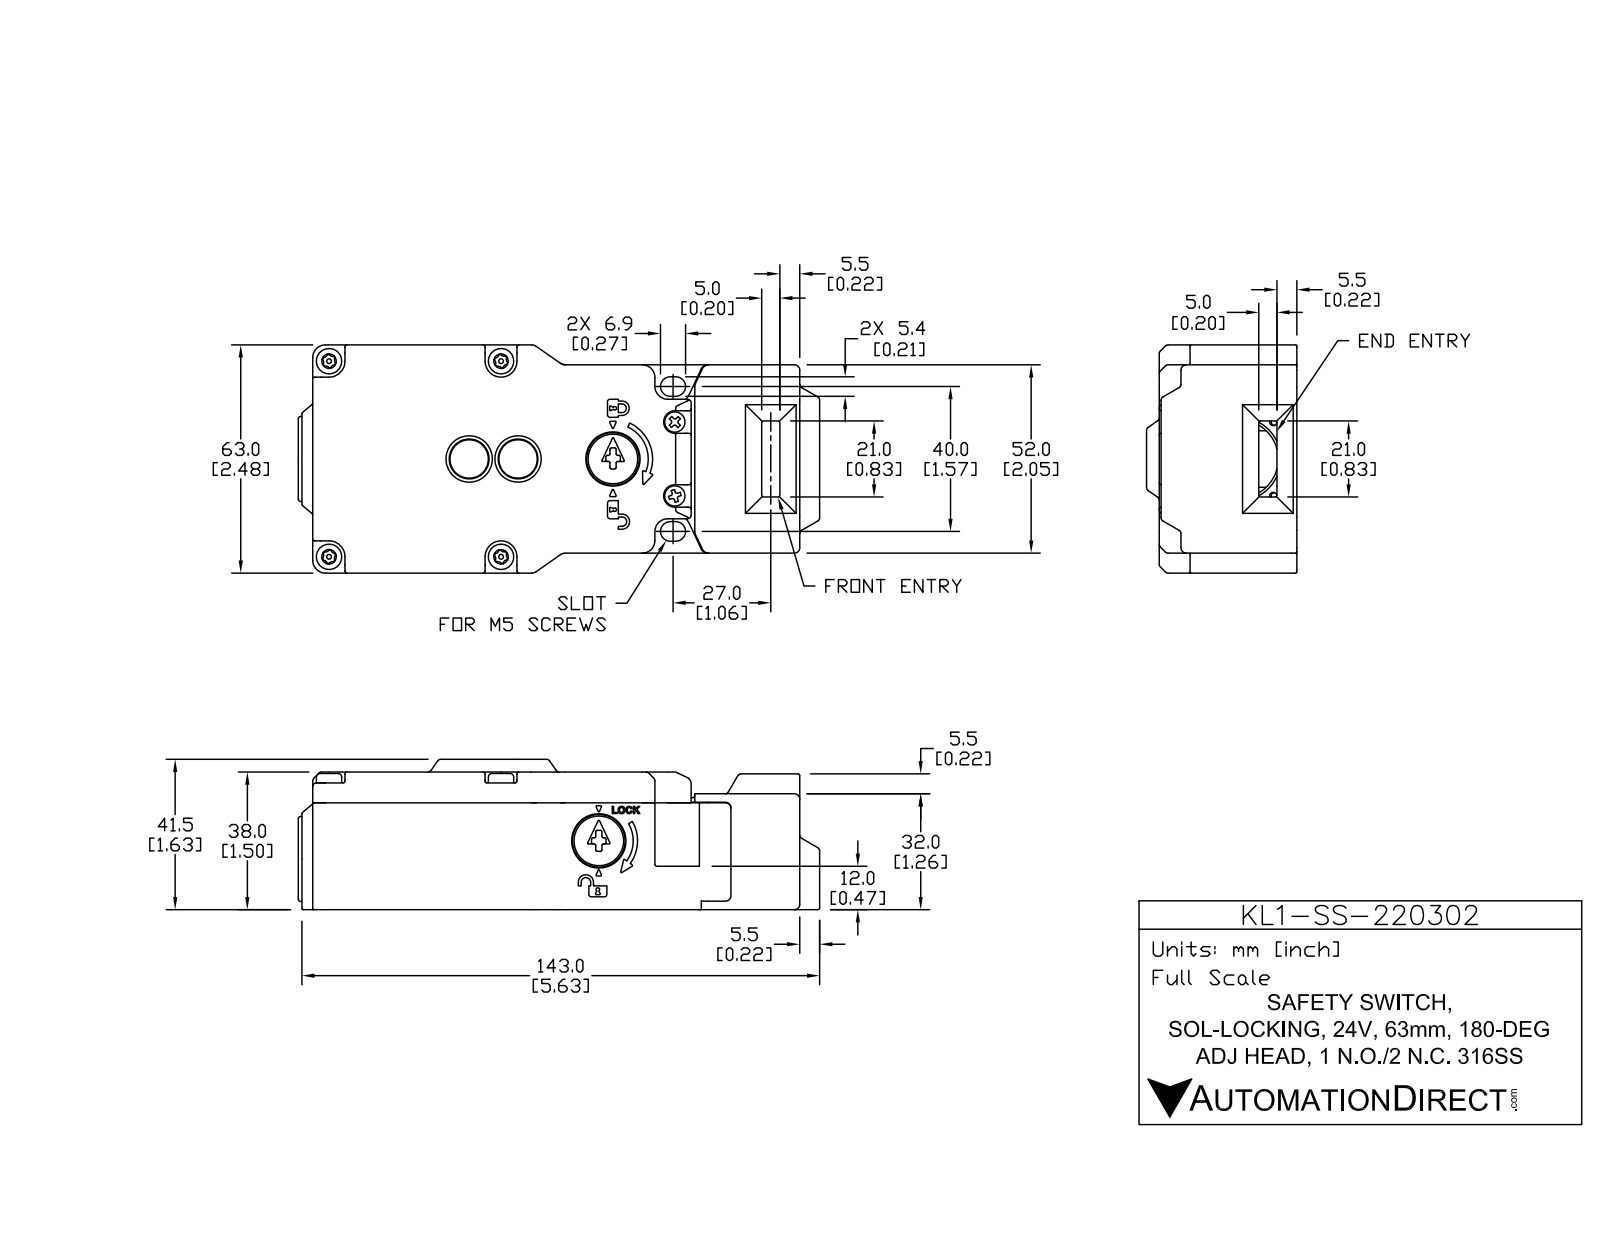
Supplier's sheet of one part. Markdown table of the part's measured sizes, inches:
| quantity | value |
| --- | --- |
| part name | KL1-SS-220302 |
| STEP written by | SolidWorks 2017 (AUTOMOTIVE_DESIGN) |
| units | inches |
| bodies | 18 solids, 3047 faces (909 planar, 1225 cylindrical, 913 other) |
| overall size | 5.669 × 2.48 × 1.634 |
| volume | 6.348 in³ |
| surface area | 118.8 in² |
| round holes (diameter × count) | 0.102 × 4, 0.134 × 4, 0.157 × 4, 0.161 × 4, 0.177 × 4, 0.197 × 4, 0.079 × 2, 0.083 × 2, 0.118 × 2, 0.126 × 2, 0.142 × 2, 0.264 × 2 |
| round bosses / shafts (diameter × count) | 0.276 × 4, 0.138 × 4, 0.051 × 4, 0.197 × 3, 0.039 × 3, 0.571 × 2, 0.417 × 2, 0.362 × 2 |
| partial cylindrical surfaces (radius × count) | 0.02 × 348, 0.012 × 126, 0.039 × 106, 0.008 × 30, 0.016 × 24, 0.059 × 16, 0.006 × 14, 0.028 × 12 |
| main face-to-face distances | 0.098, 0.118, 0.217, 1.496, 1.398, 1.402, 1.303, 0.094, 2.264, 2.146 |
| hole center spacings | 0.404, 0.498, 0.515, 0.549, 0.784, 0.803, 1.079, 1.118 |
